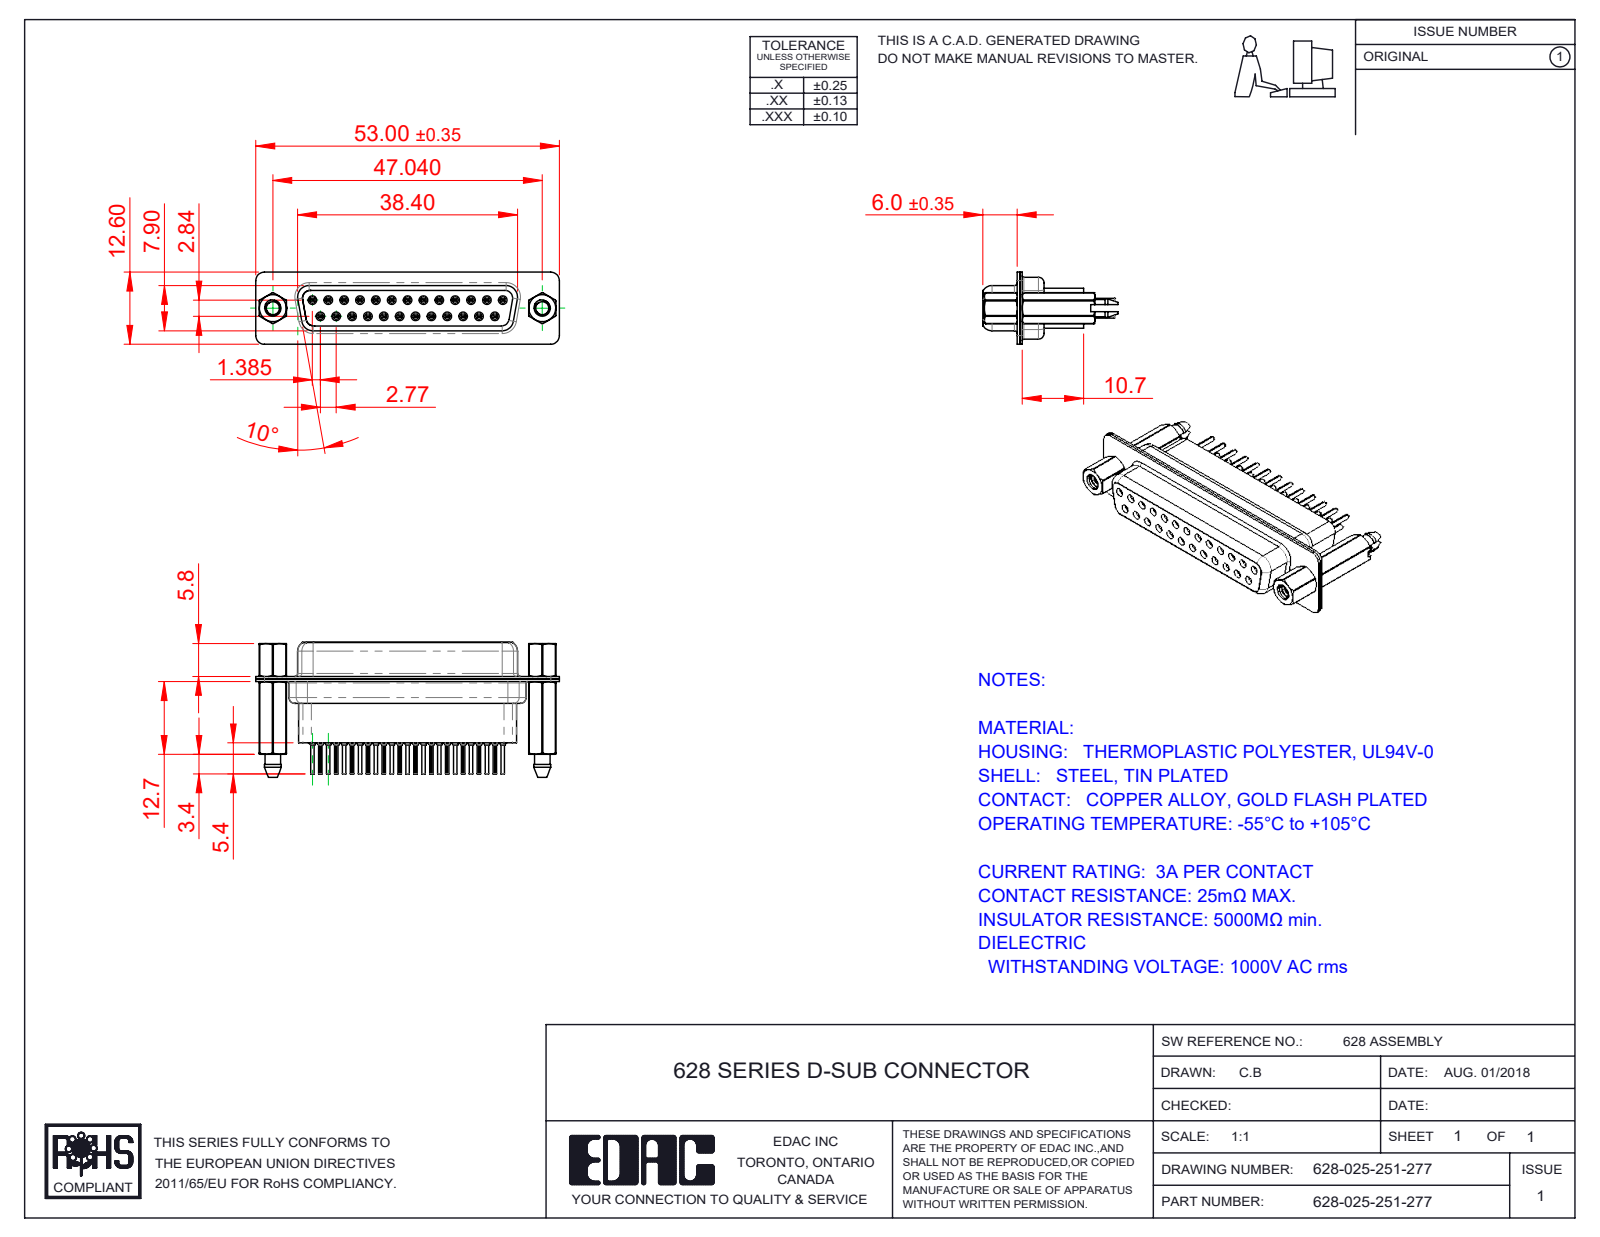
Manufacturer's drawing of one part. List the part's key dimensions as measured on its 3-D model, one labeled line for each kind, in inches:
Part name (STEP PRODUCT): 628-025-251-277; 628 Shell Rear_25 Contacts; 628 Housing_25 HP; 628 4-40 Hex Standoff (+4 more)
STEP written by: SolidWorks 2020 (CONFIG_CONTROL_DESIGN)
Units: inches
Bodies: 32 solids, 3554 faces (896 planar, 1066 cylindrical, 1592 other)
Overall size (bounding box): 2.087 × 0.929 × 0.496
Volume: 0.337 in³ · Surface area: 19.61 in²
Round holes (diameter × count): ⌀0.008 ×25, ⌀0.031 ×25, ⌀0.035 ×25, ⌀0.043 ×25, ⌀0.063 ×25, ⌀0.067 ×13, ⌀0.089 ×2, ⌀0.09 ×2, ⌀0.157 ×2, ⌀0.159 ×2, ⌀0.191 ×2
Round bosses / shafts (diameter × count): ⌀0.079 ×25, ⌀0.059 ×25, ⌀0.047 ×25, ⌀0.024 ×25, ⌀0.195 ×2, ⌀0.189 ×2, ⌀0.11 ×2
Partial cylindrical surfaces — rounded edges, fillets, slot ends (radius × count): R0.004 ×50, R0.011 ×25, R0.059 ×18, R0.079 ×12, R0.053 ×6, R0.063 ×6, R0.01 ×4, R0.02 ×4
Main face-to-face distances: 0.018, 0.016, 0.26, 0.335, 0.075, 0.276, 0.035, 0.055, 0.278, 0.187
Hole centre spacings: 0.124, 0.327, 0.109, 0.218, 0.436, 0.654, 0.198, 0.198
